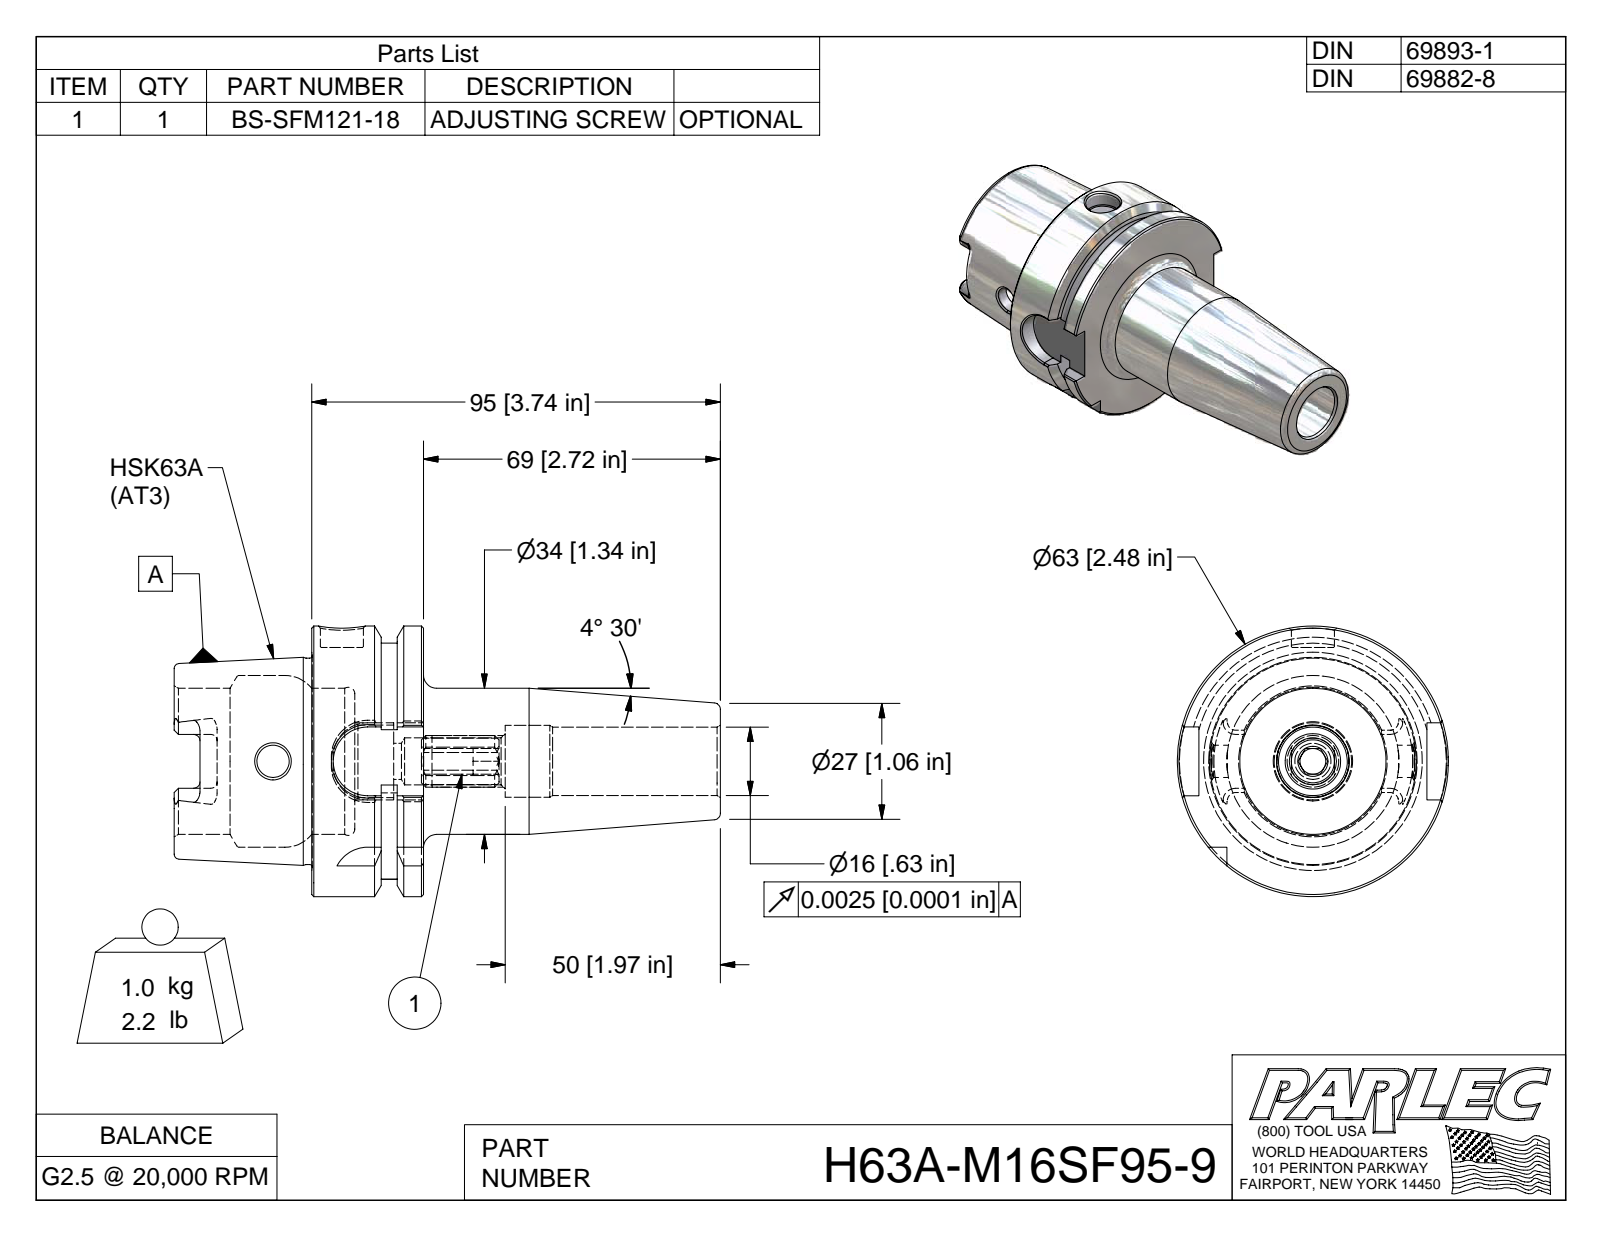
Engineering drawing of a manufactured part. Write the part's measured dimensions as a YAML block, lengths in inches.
part_name: "H63A-M16SF95-9; H63A-M16SF95-9-1; BS-SFM121-18"
step_written_by: "Autodesk Inventor 2009 (AUTOMOTIVE_DESIGN)"
units: inches
bodies: {solids: 2, faces: 157, planar: 58, cylindrical: 35, other: 64}
overall_size: [5, 2.48, 2.48]
volume: 7.682
surface_area: 51.14
round_holes:
  - {diameter: 0.295, count: 1}
  - {diameter: 0.394, count: 1}
  - {diameter: 0.629, count: 1}
  - {diameter: 0.659, count: 1}
  - {diameter: 0.666, count: 1}
  - {diameter: 1.339, count: 1}
  - {diameter: 1.575, count: 1}
round_bosses_or_shafts:
  - {diameter: 2.48, count: 1}
  - {diameter: 1.891, count: 1}
partial_cylinders:
  - {radius: 0.059, count: 6}
  - {radius: 0.113, count: 4}
  - {radius: 0.315, count: 4}
  - {radius: 0.236, count: 1}
  - {radius: 1.083, count: 1}
face_to_face_distances: [1.024, 0.394, 0.241, 0.389, 0.63, 1.26, 1.654, 2.283, 1.894, 0.635]
